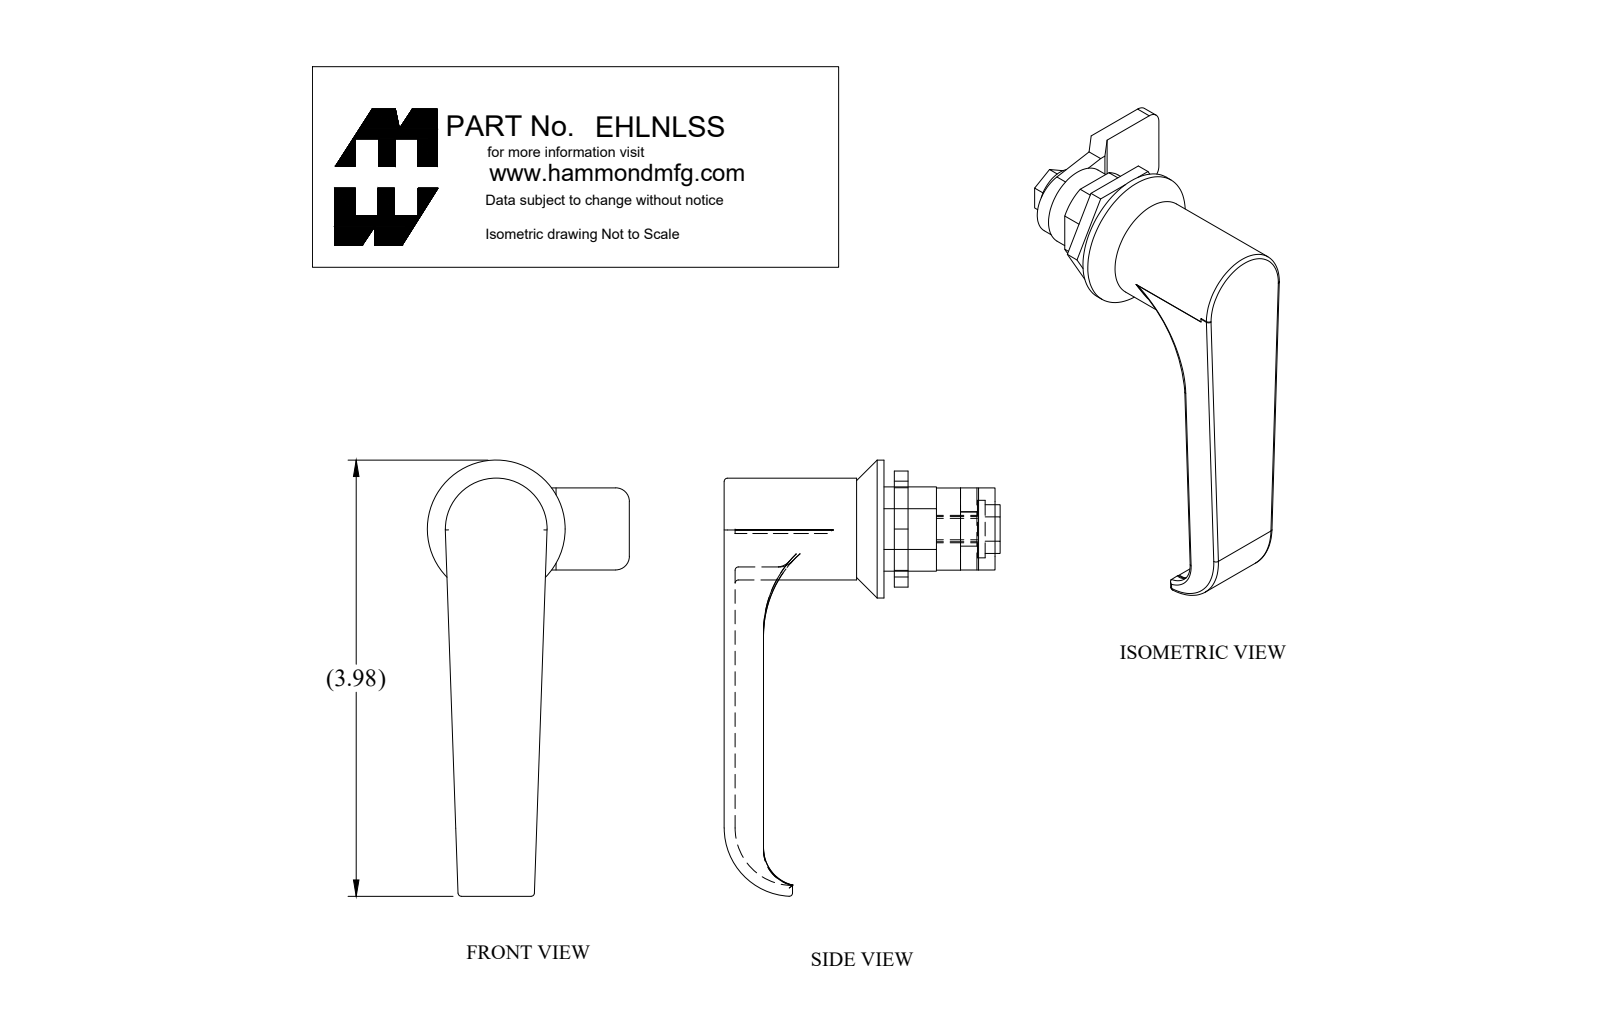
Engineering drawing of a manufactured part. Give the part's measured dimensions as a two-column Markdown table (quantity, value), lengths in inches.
| quantity | value |
| --- | --- |
| part name | EHLNLSS_Default |
| STEP written by | SolidWorks 2018 (CONFIG_CONTROL_DESIGN) |
| units | inches |
| bodies | 4 solids, 143 faces (63 planar, 46 cylindrical, 34 other) |
| overall size | 3.985 × 2.523 × 1.847 |
| volume | 2.119 in³ |
| surface area | 23.02 in² |
| round holes (diameter × count) | 0.196 × 1, 0.755 × 1 |
| round bosses / shafts (diameter × count) | 1.26 × 1, 0.93 × 1, 0.75 × 1, 0.525 × 1, 0.232 × 1 |
| partial cylindrical surfaces (radius × count) | 0.03 × 15, 0.125 × 2, 0.307 × 1, 0.327 × 1, 0.35 × 1, 0.427 × 1, 0.525 × 1, 0.625 × 1 |
| main face-to-face distances | 0.1, 0.15, 0.77, 0.165, 0.22, 1.361, 1.461, 0.48, 0.7, 2.061 |
